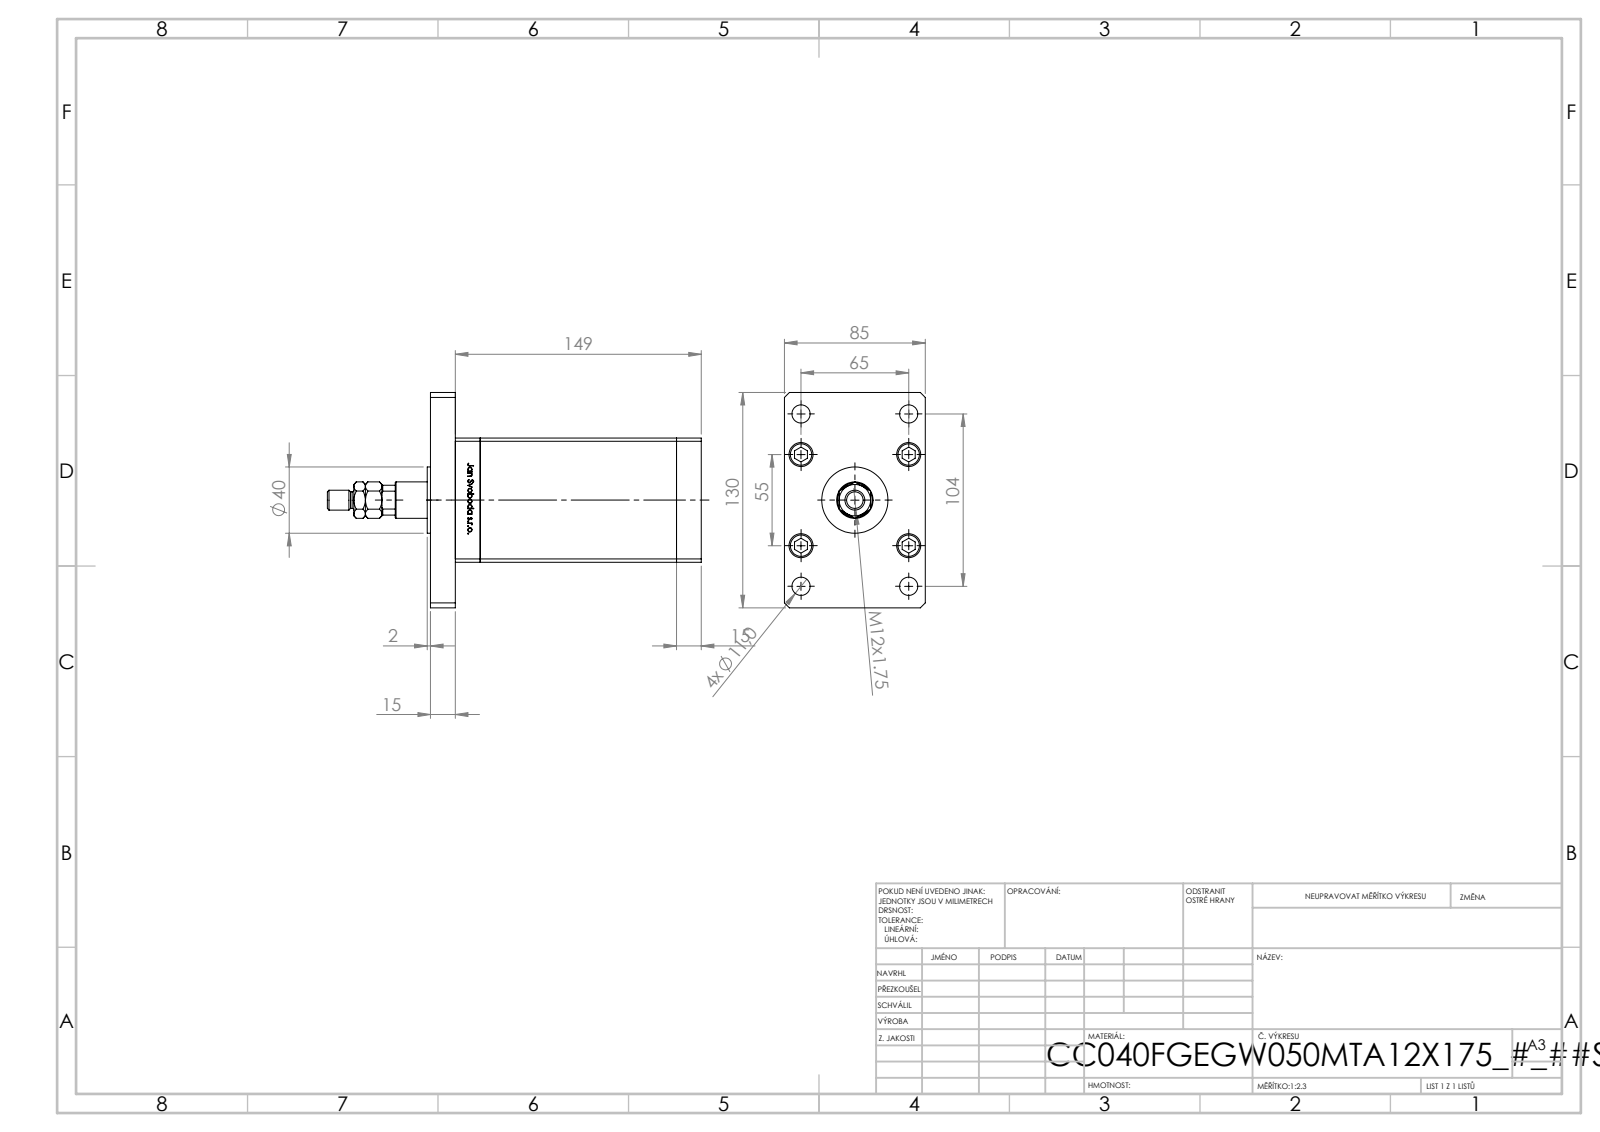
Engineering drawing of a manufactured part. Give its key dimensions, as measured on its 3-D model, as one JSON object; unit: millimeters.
{"part_name": "V220C_FRONT_F; V220C_F_MIDDLE; V220C_VC_F; V220C BACK_F (+3 more)", "step_written_by": "SolidWorks 2019 (CONFIG_CONTROL_DESIGN)", "units": "millimeters", "bodies": {"solids": 20, "faces": 1359, "planar": 532, "cylindrical": 191, "other": 636}, "overall_size": [225.8, 130, 85], "volume_mm3": 1009000, "surface_area_mm2": 186140, "round_holes": [[11, 9], [15.5, 5], [10, 4], [14.5, 4], [2, 2], [13.16, 2], [13.5, 1], [22, 1], [23.5, 1]], "round_bosses_or_shafts": [[8, 9], [14.5, 5], [40, 1], [12, 1], [10, 1]], "partial_cylinders_radius": [[0.93, 2], [10.5, 1]], "face_to_face_distances": [15, 133.5, 148.5, 85, 30, 75, 118.5, 163.5, 10.5, 110.7], "hole_center_spacings": [28, 24.5, 42.57, 61.32, 65, 69.46, 79.5, 102.69]}
